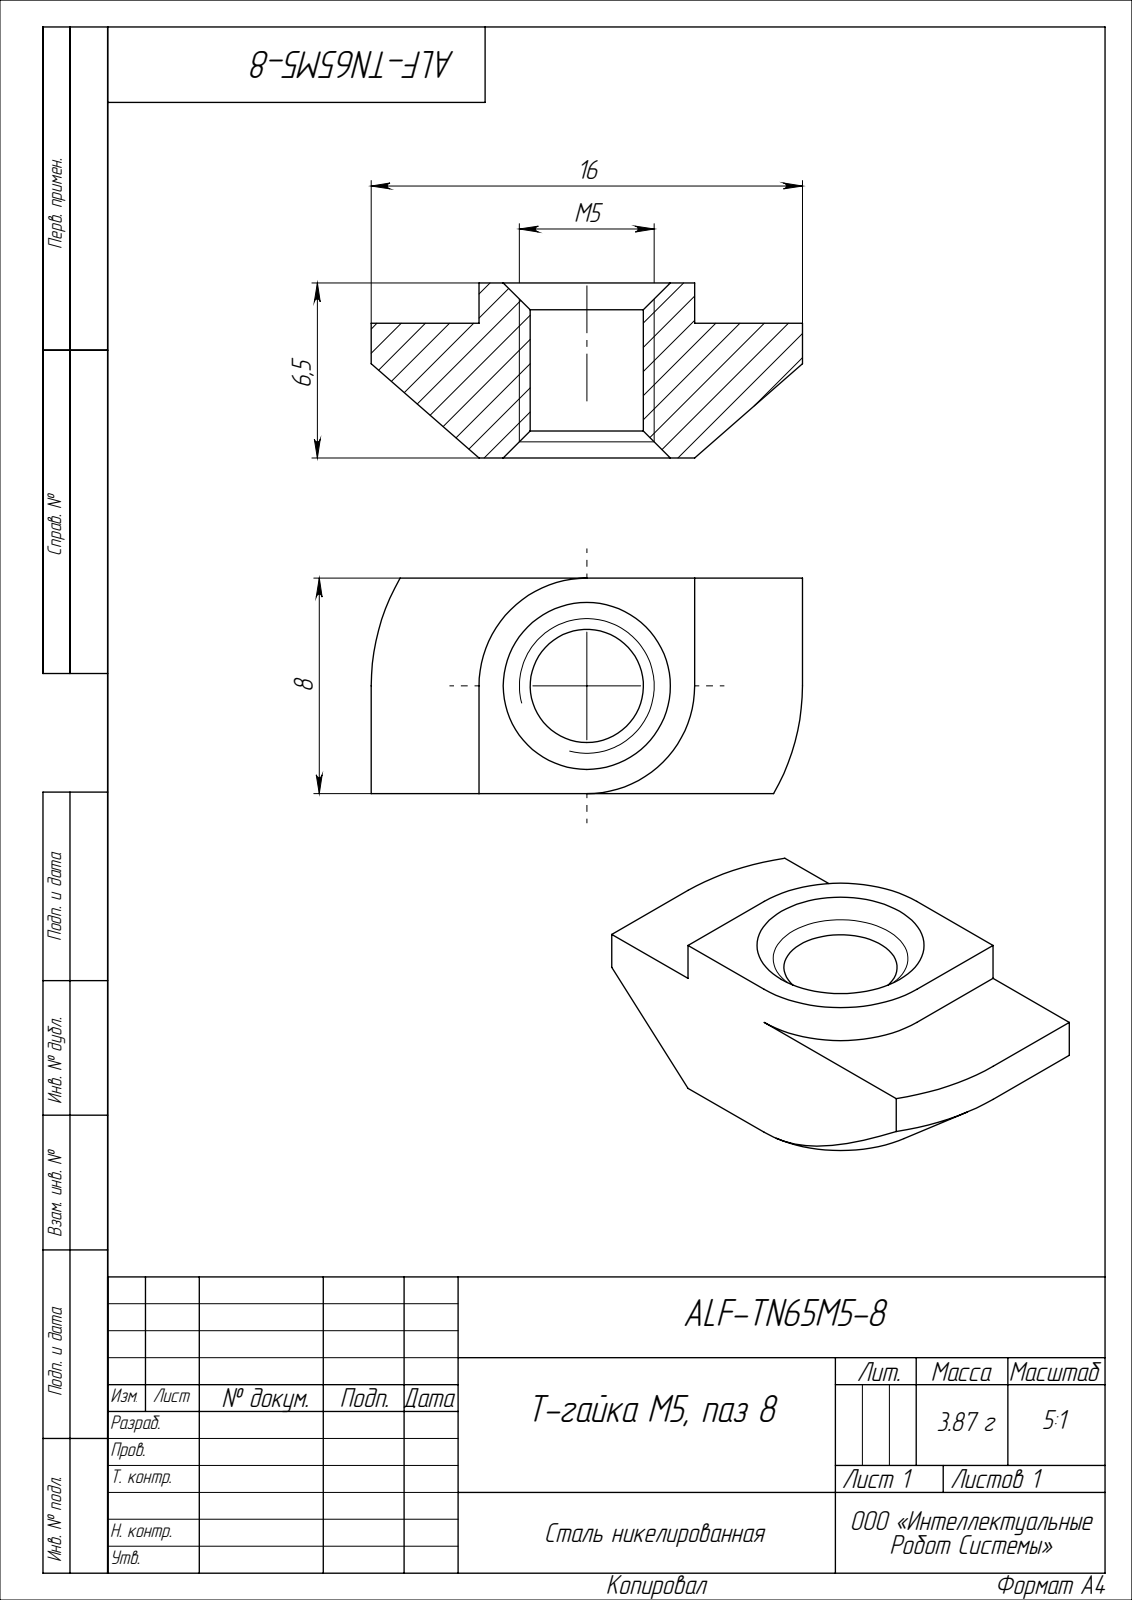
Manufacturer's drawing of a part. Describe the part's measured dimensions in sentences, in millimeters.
The part is named "ALF-TN65М5-8". Its 3-D file was written by "SolidWorks 2022 (CONFIG_CONTROL_DESIGN)". It is 1 solid with 24 faces: 12 planar, 6 cylindrical and 6 other. Overall it measures 16 by 8 by 6.5 millimeters. Its volume is 490 cubic millimeters and its surface area 502 square millimeters. Round holes: 1 of diameter 4.2. Partial cylindrical surfaces (rounded edges, fillets, slot ends): 1 of radius 4, 1 of radius 8. The main face-to-face distances are 8, 5, 6.5, 1.5, 12, 4, 16.
